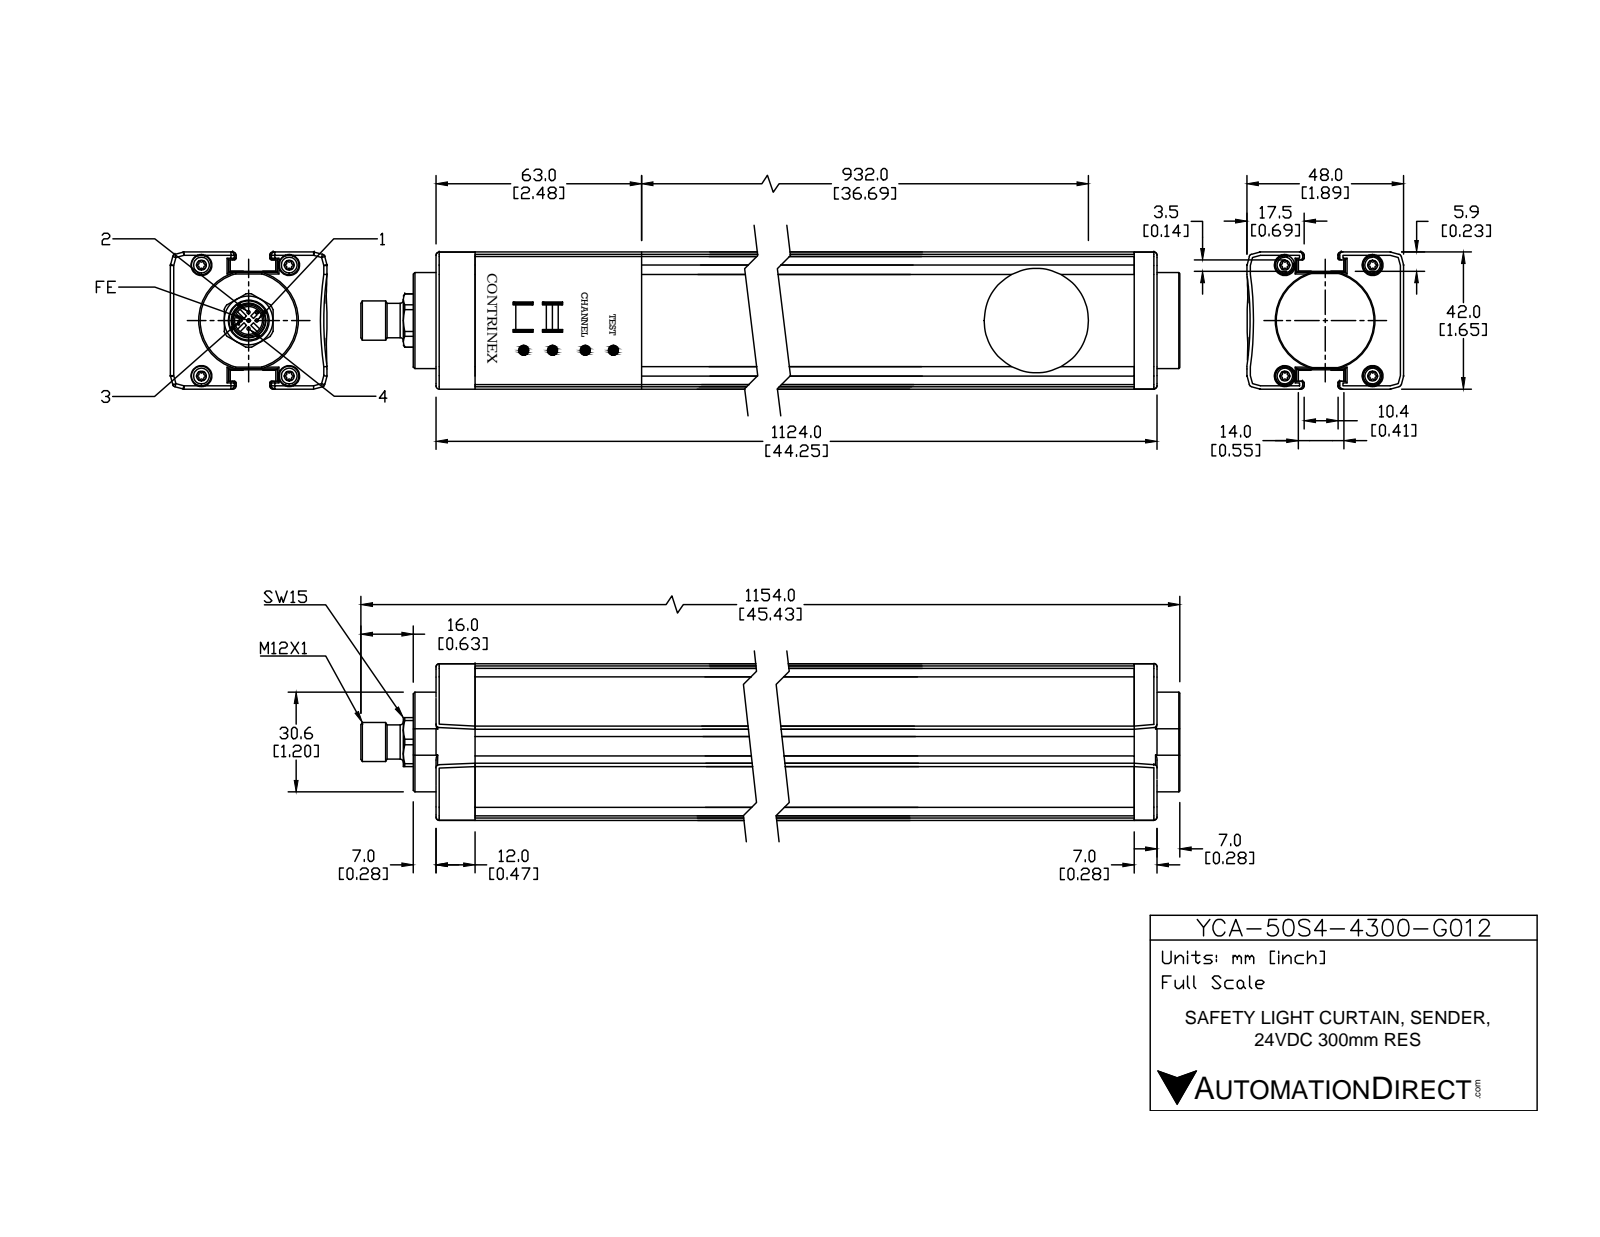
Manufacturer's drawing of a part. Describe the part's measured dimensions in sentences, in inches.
The part is named "YCA-50S4-4300-G012". Its 3-D file was written by "SolidWorks 2016 (AUTOMOTIVE_DESIGN)". It is 18 solids with 454 faces: 221 planar, 172 cylindrical and 61 other. Overall it measures 45.433 by 1.89 by 1.654 inches. Its volume is 123.6 cubic inches and its surface area 402.3 square inches. Round holes: 4 of diameter 0.236, 1 of diameter 0.039, 1 of diameter 0.335, 1 of diameter 1.26. Round bosses or shafts: 4 of diameter 0.217, 4 of diameter 0.039, 1 of diameter 1.205, 1 of diameter 0.472, 1 of diameter 0.413. Partial cylindrical surfaces (rounded edges, fillets, slot ends): 52 of radius 0.039, 4 of radius 0.02, 1 of radius 0.323, 1 of radius 3.937. The main face-to-face distances are 1.654, 0.228, 1.425, 1.157, 0.039, 0.268, 1.386, 1.197, 0.551, 0.677. The hole center spacings are 0.828, 0.88, 1.059, 1.339, 1.707.
